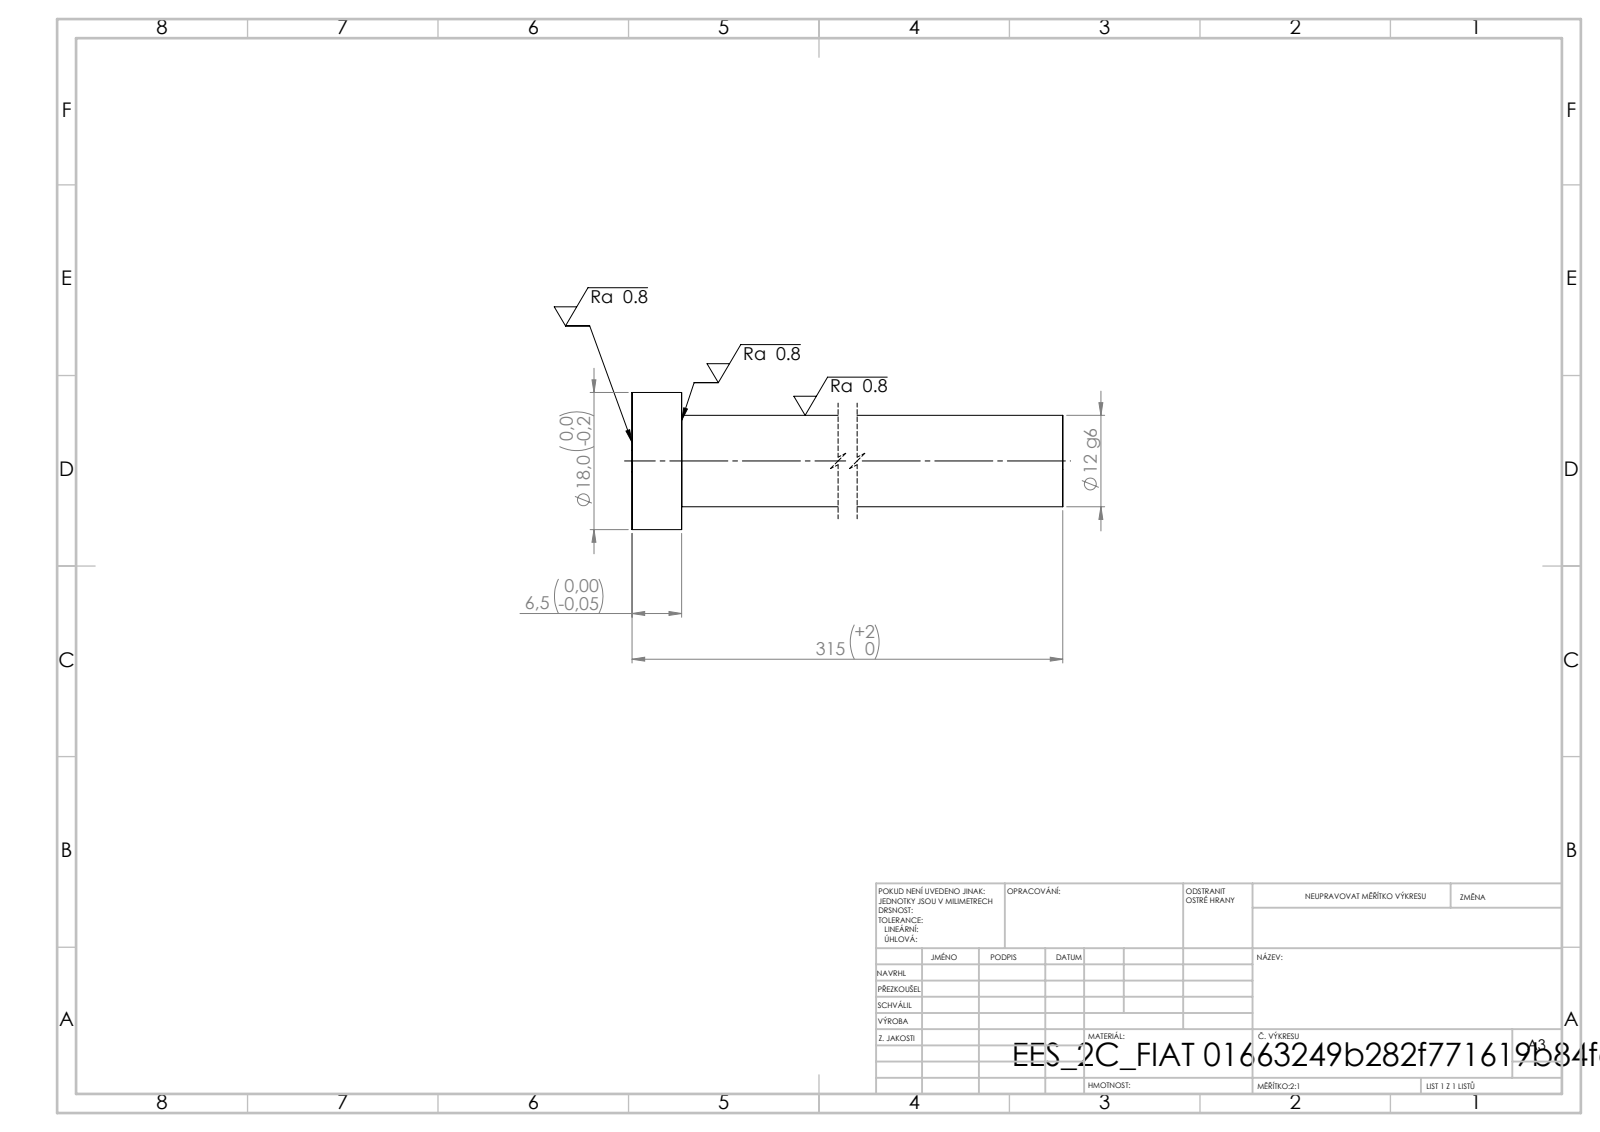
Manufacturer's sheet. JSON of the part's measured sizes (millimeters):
{"step_written_by": "SolidWorks 2019 (CONFIG_CONTROL_DESIGN)", "units": "millimeters", "bodies": {"solids": 1, "faces": 7, "planar": 3, "cylindrical": 4, "other": 0}, "overall_size": [315, 18, 18], "volume_mm3": 36545, "surface_area_mm2": 12507, "round_bosses_or_shafts": [[18, 1], [12, 1]], "face_to_face_distances": [6.5, 315, 308.5]}
